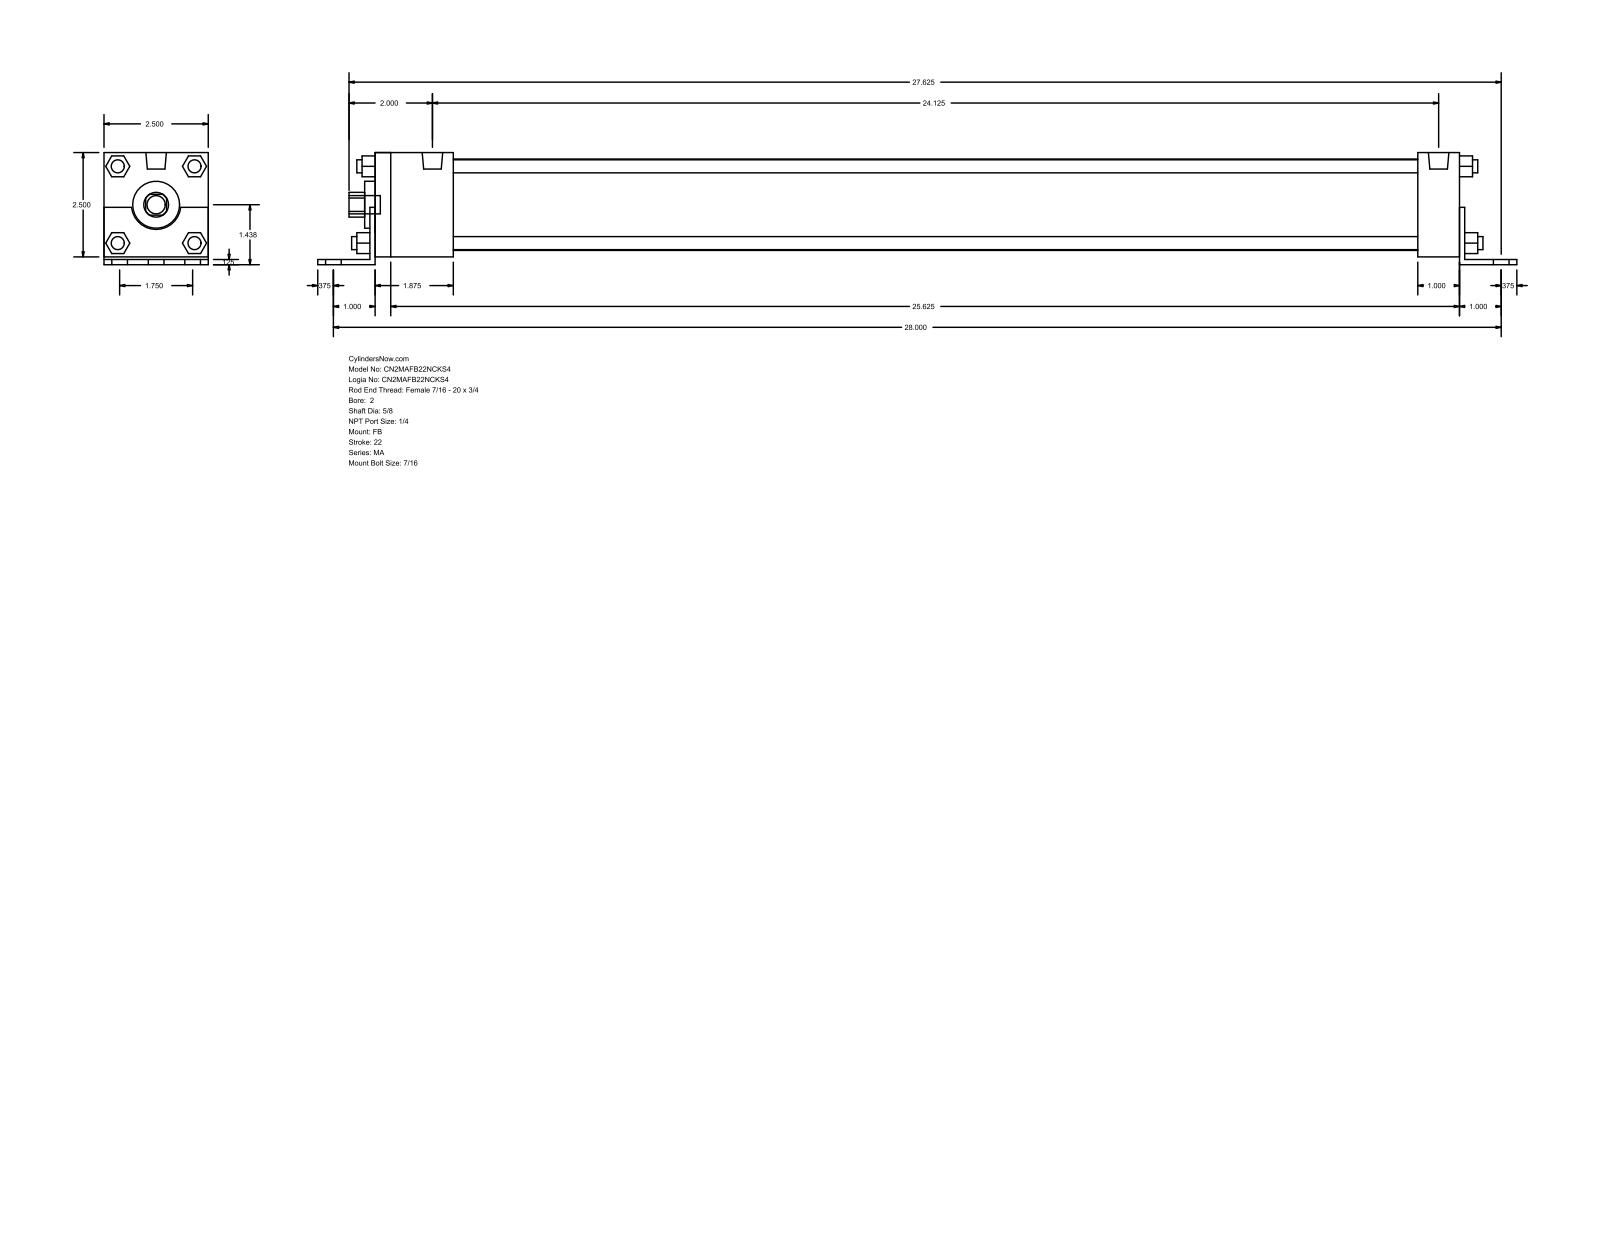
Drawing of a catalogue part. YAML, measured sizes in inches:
part_name: "MA_FB__0200_0.625"
step_written_by: "GSSL Pune (CONFIG_CONTROL_DESIGN)"
units: inches
bodies: {solids: 0, faces: 140, planar: 105, cylindrical: 35, other: 0}
overall_size: [28.75, 2.687, 2.5]
round_holes:
  - {diameter: 0.625, count: 1}
  - {diameter: 1.125, count: 1}
  - {diameter: 2.19, count: 1}
round_bosses_or_shafts:
  - {diameter: 0.313, count: 8}
  - {diameter: 0.437, count: 7}
  - {diameter: 0.492, count: 2}
partial_cylinders:
  - {radius: 0.297, count: 1}
  - {radius: 0.593, count: 1}
face_to_face_distances: [2.5, 0.187, 0.125, 2.687, 0.063, 0.125, 2.563, 26.125, 26, 0.5]
